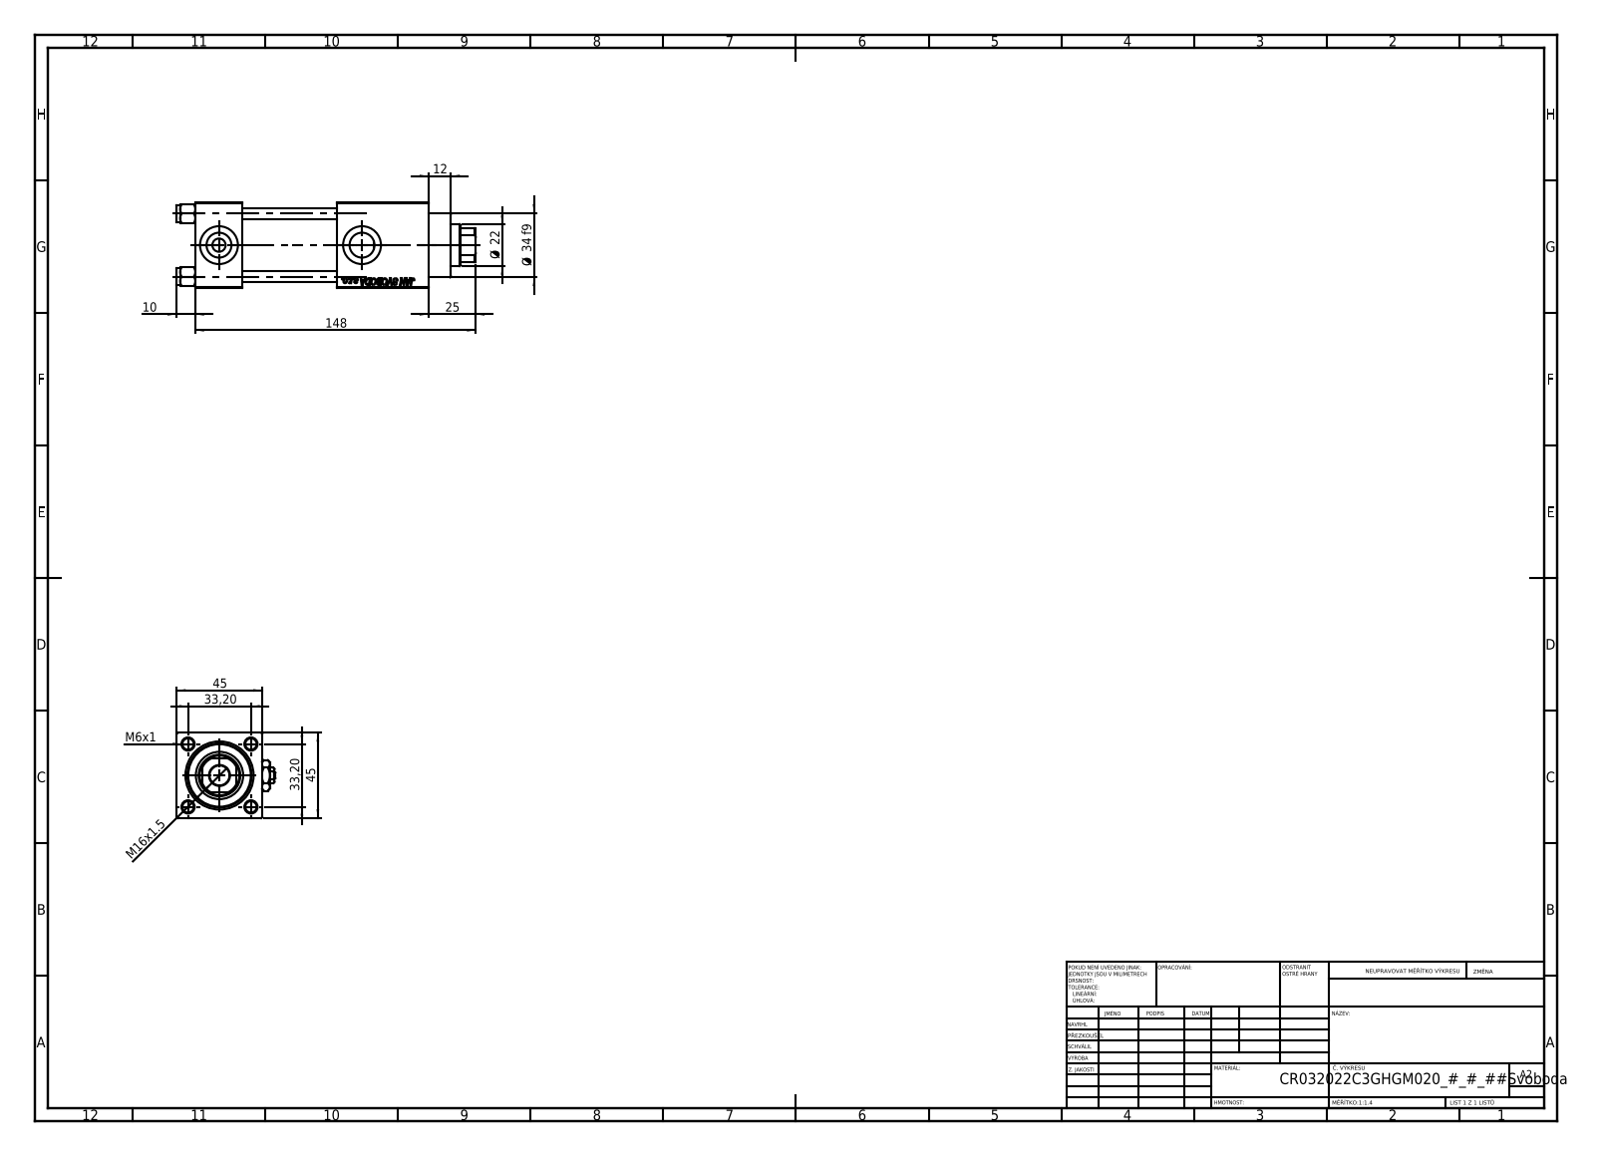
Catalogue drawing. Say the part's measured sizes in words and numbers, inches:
The part is named "NUT_M5_C; V215CR_C_Body; V215CR_VCP_C; V215CR_C_TYCINKA (+2 more)". Its 3-D file was written by "SolidWorks 2019 (CONFIG_CONTROL_DESIGN)". It is 13 solids with 1248 faces: 572 planar, 98 cylindrical and 578 other. Overall it measures 6.22 by 2.047 by 1.772 inches. Its volume is 12.71 cubic inches and its surface area 113.4 square inches. Round holes: 4 of diameter 0.236, 2 of diameter 0.276, 2 of diameter 0.518, 2 of diameter 0.787, 1 of diameter 0.413, 1 of diameter 0.866, 1 of diameter 0.945, 1 of diameter 0.984, 1 of diameter 1.26, 1 of diameter 1.299. Round bosses or shafts: 4 of diameter 0.354, 1 of diameter 1.496, 1 of diameter 1.339. Partial cylindrical surfaces (rounded edges, fillets, slot ends): 1 of radius 0.413. The main face-to-face distances are 1.772, 0.984, 1.969, 4.843, 2.953, 3.858, 1.764, 1.89, 3.713, 2.728. The hole center spacings are 0.924, 1.307, 1.848, 2.972.
